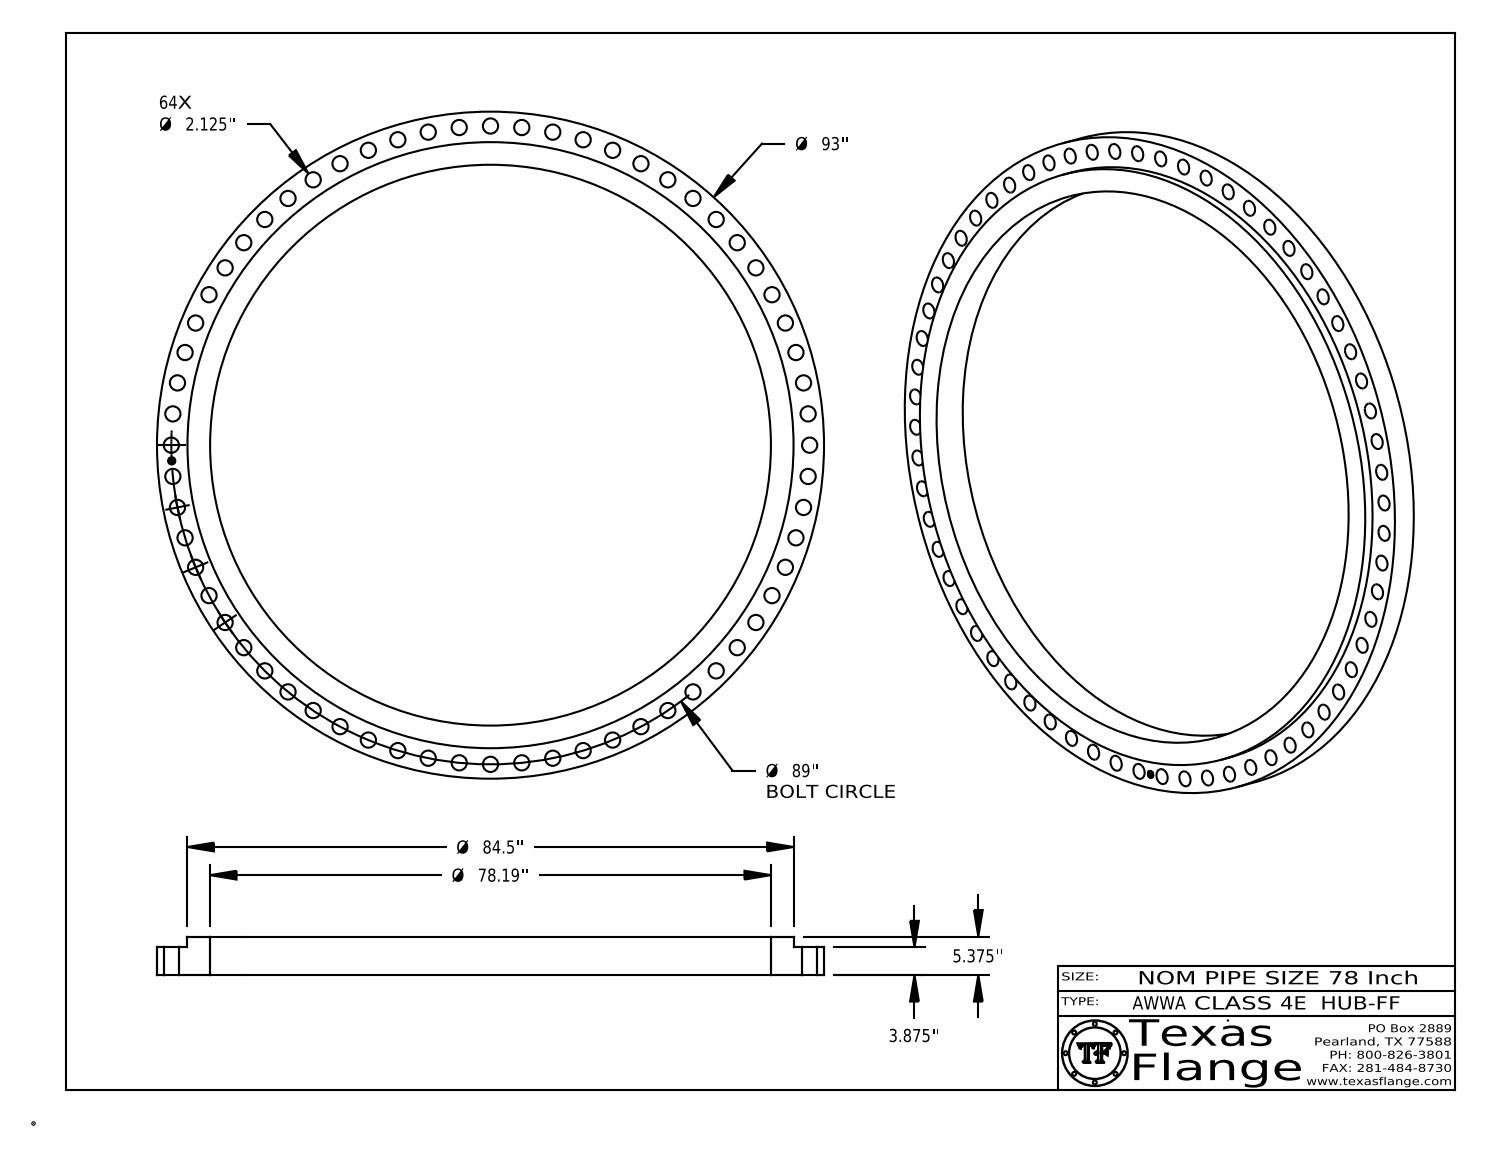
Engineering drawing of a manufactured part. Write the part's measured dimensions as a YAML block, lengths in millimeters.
part_name: "AWWA Class 4E-HUB-FF"
step_written_by: "CATIA V5 STEP AP214 (AUTOMOTIVE_DESIGN)"
units: millimeters
bodies: {solids: 1, faces: 522, planar: 368, cylindrical: 154, other: 0}
overall_size: [2362.2, 2362.2, 136.5]
volume: 131900000
surface_area: 5184000
round_holes:
  - {diameter: 54, count: 64}
  - {diameter: 25.4, count: 1}
  - {diameter: 1986, count: 1}
round_bosses_or_shafts:
  - {diameter: 1.5, count: 8}
  - {diameter: 2362.2, count: 1}
  - {diameter: 2146.3, count: 1}
  - {diameter: 20, count: 1}
face_to_face_distances: [98.4, 136.5, 38.1, 98, 0.4, 38.5, 7.6, 7.4, 1.4, 4.9]
hole_center_spacings: [110.9, 441, 1130.3, 221.6, 331.7, 549.3, 656.2, 761.6]
